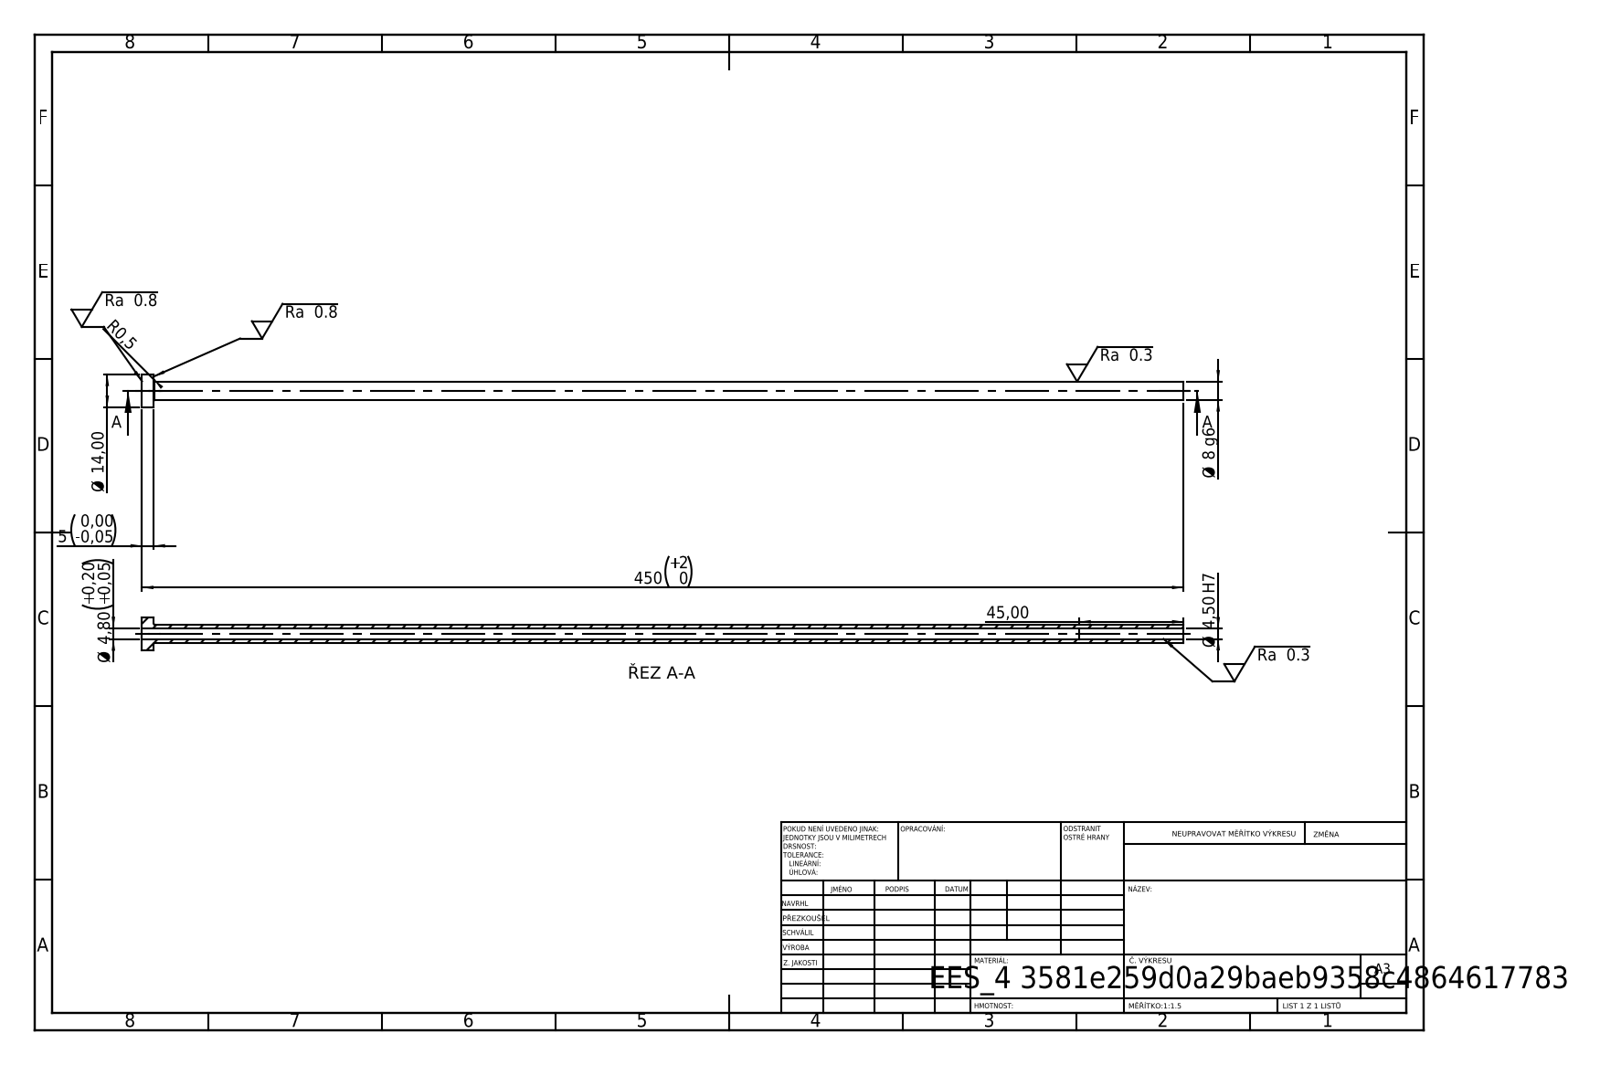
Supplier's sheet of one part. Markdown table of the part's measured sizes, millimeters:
| quantity | value |
| --- | --- |
| STEP written by | SolidWorks 2019 (CONFIG_CONTROL_DESIGN) |
| units | millimeters |
| bodies | 1 solid, 14 faces (4 planar, 8 cylindrical, 2 other) |
| overall size | 450 × 14 × 14 |
| volume | 15 095 mm³ |
| surface area | 18 418 mm² |
| round holes (diameter × count) | 4.5 × 1, 4.8 × 1 |
| round bosses / shafts (diameter × count) | 14 × 1, 8 × 1 |
| main face-to-face distances | 5, 450, 445, 405, 400, 45 |
